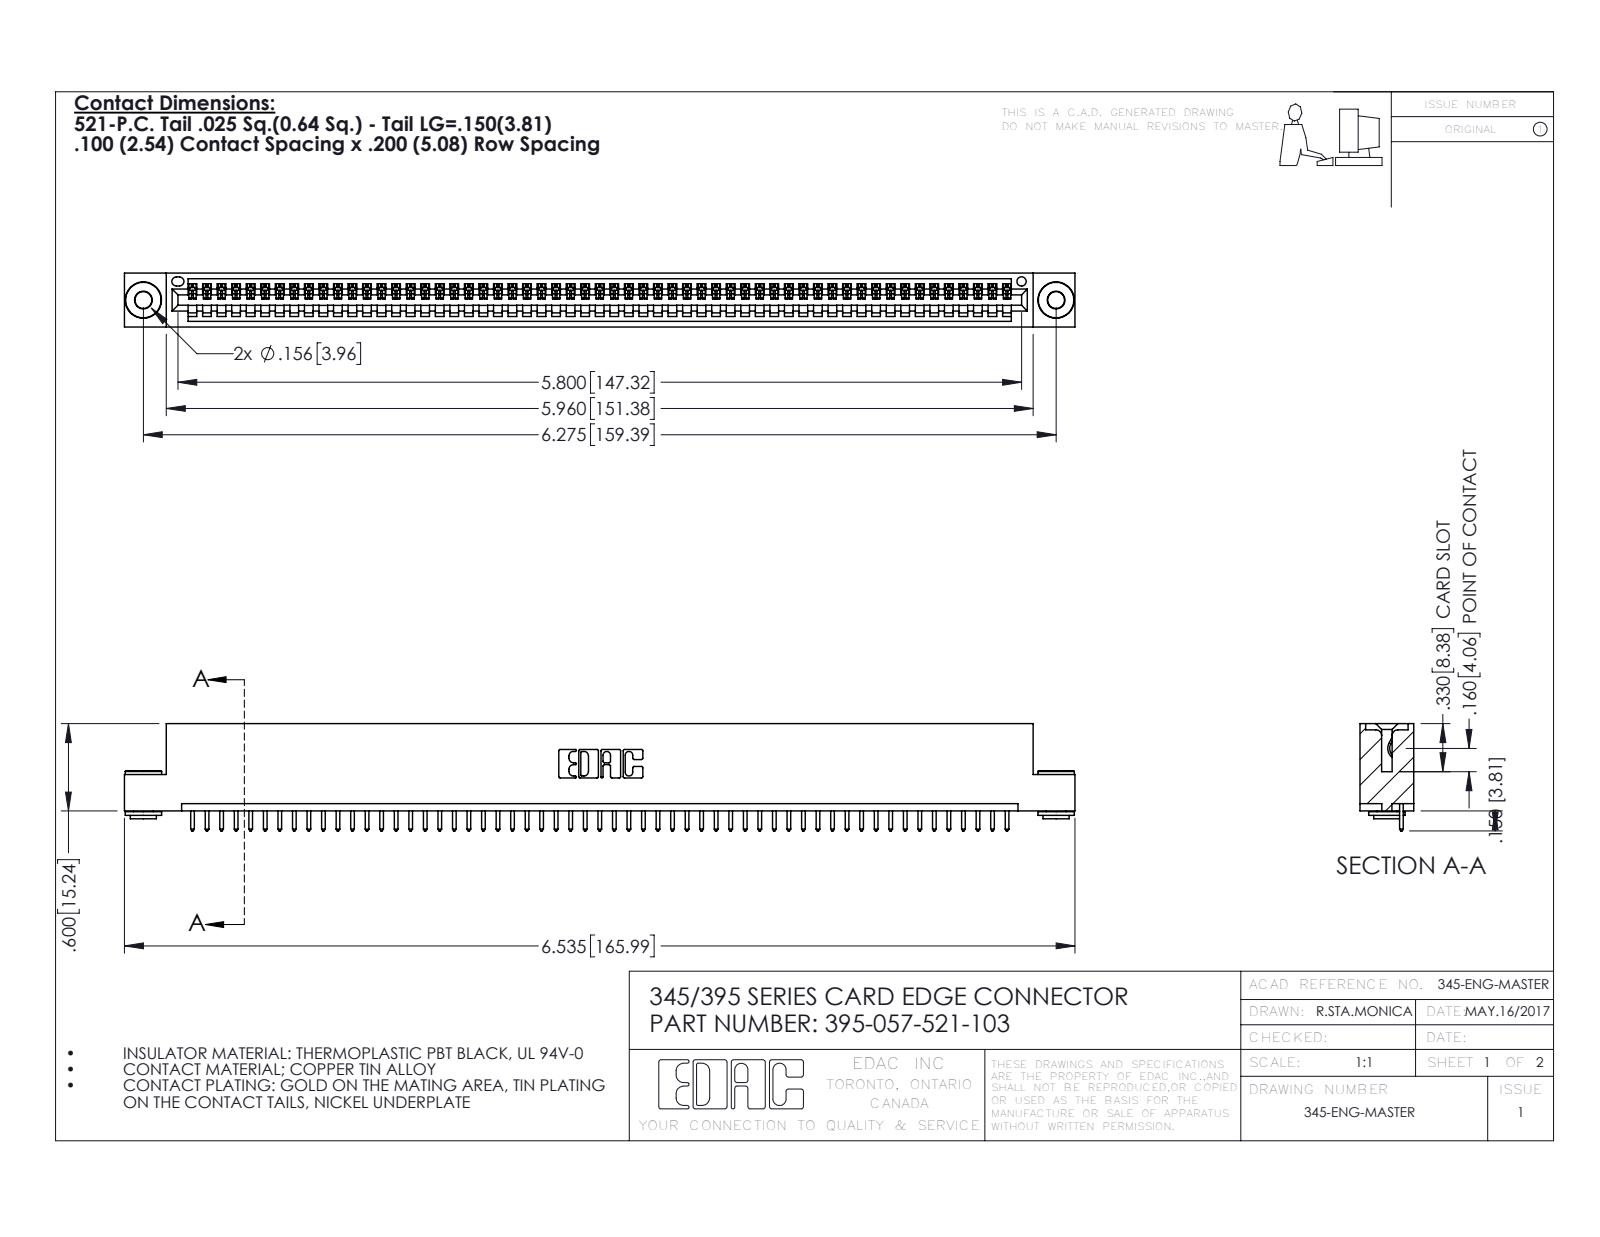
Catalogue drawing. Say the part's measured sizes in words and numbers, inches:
The part is named "395-057-521-103; 345-250-002_345-250-002-102; 345 Part_Flush Mounting Lugs - 0.156 Dia-TH; 345-292-001_345-293-121". Its 3-D file was written by "SolidWorks 2016 (CONFIG_CONTROL_DESIGN)". It is 60 solids with 3470 faces: 2370 planar, 1092 cylindrical and 8 other. Overall it measures 6.535 by 0.737 by 0.37 inches. Its volume is 0.961 cubic inches and its surface area 32.1 square inches. Round holes: 2 of diameter 0.116, 2 of diameter 0.156, 1 of diameter 0.064. Round bosses or shafts: 2 of diameter 0.25, 2 of diameter 0.18, 2 of diameter 0.136. Partial cylindrical surfaces (rounded edges, fillets, slot ends): 114 of radius 0.006, 114 of radius 0.01, 22 of radius 0.01, 6 of radius 0.007, 6 of radius 0.031, 3 of radius 0.026, 2 of radius 0.031, 2 of radius 0.04. The main face-to-face distances are 0.072, 0.298, 0.37, 0.2, 0.025, 0.098, 0.272, 0.225, 0.149, 0.072. The hole center spacings are 0.27, 6.039, 6.275.
